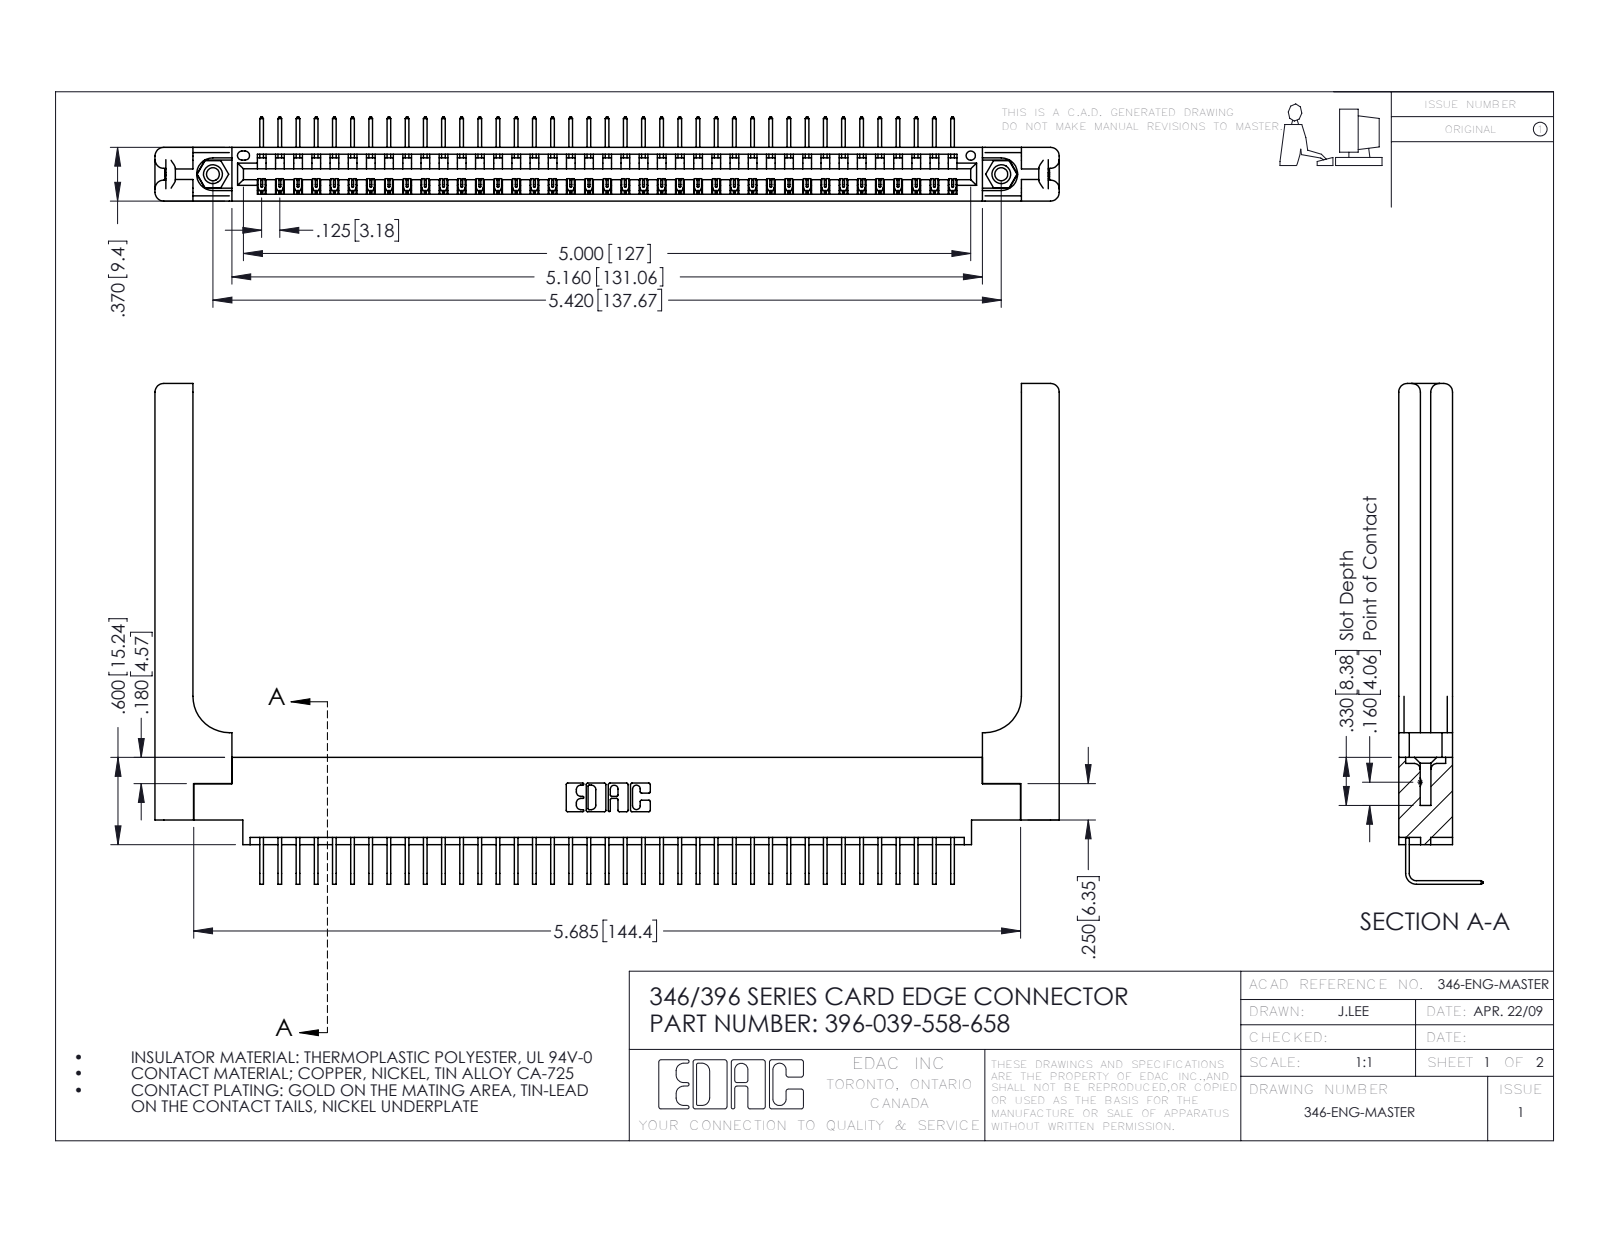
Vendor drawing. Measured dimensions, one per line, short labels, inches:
name: 396-039-558-658; 345-250-001_345-250-001-102; 345-292-001_558 Tail - 2; 346 Part_0.170 Offset - 0.156 Dia-TH (+1 more)
written by: SolidWorks 2016 (CONFIG_CONTROL_DESIGN)
unit: in
bodies: 44 solids, 2722 faces (1866 planar, 796 cylindrical, 60 other)
size: 6.216 × 3.443 × 0.58
volume: 1.378 in³; area: 38.6 in²
holes: 2× ⌀0.089, 2× ⌀0.125, 2× ⌀0.156, 1× ⌀0.064
bosses: 2× ⌀0.155
rounds: 78× R0.006, 22× R0.01, 16× R0.06, 6× R0.007, 6× R0.031, 3× R0.026, 2× R0.03, 2× R0.031
face distances: 0.37, 0.322, 0.048, 0.072, 0.148, 0.15, 0.025, 0.298, 0.25, 0.222
hole spacings: 0.246, 5.211, 5.42
